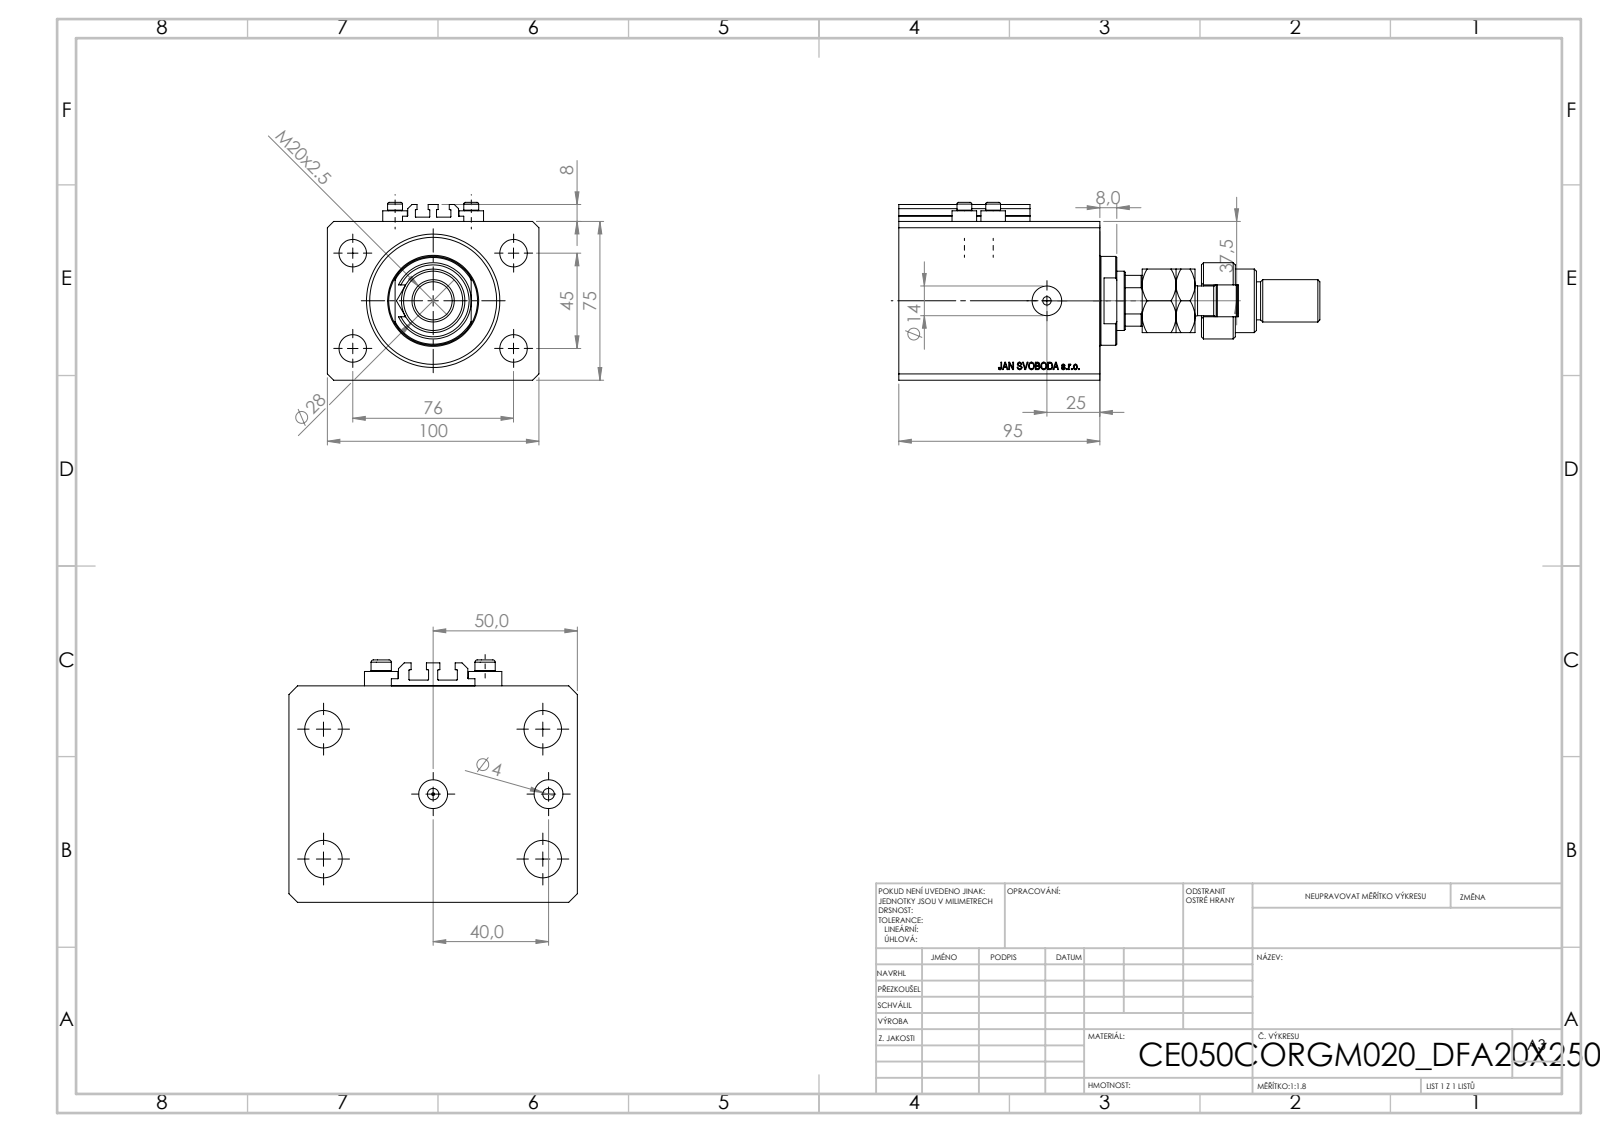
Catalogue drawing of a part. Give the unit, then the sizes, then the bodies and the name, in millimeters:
Units: millimetres
Overall size (bounding box): 199 × 100 × 84
Round holes (diameter × count): ⌀4 ×8, ⌀13 ×4, ⌀10 ×2, ⌀14 ×2, ⌀1.25 ×1, ⌀18.5 ×1, ⌀28 ×1, ⌀50 ×1, ⌀63 ×1
Round bosses / shafts (diameter × count): ⌀11.6 ×4, ⌀7 ×4, ⌀42 ×1, ⌀36 ×1, ⌀30 ×1, ⌀22 ×1, ⌀20 ×1, ⌀18 ×1
Partial cylindrical surfaces — rounded edges, fillets, slot ends (radius × count): R0.2 ×10, R7.5 ×1, R12 ×1, R13.5 ×1
Main face-to-face distances: 75, 100, 20, 95, 11.9, 83.1, 63.1, 40, 30, 55
Hole centre spacings: 44.16, 45, 13.6, 22.59, 36, 38.48, 76, 81.18
Volume: 696 556 mm³ · Surface area: 130 719 mm²
Bodies: 10 solids, 1123 faces (532 planar, 101 cylindrical, 490 other)
Part name (STEP PRODUCT): MFA; V250CE_C_VCP; FEMALE_PART_FOR_DFA; ALLEN BOLT V250CE (+2 more)
STEP written by: SolidWorks 2019 (CONFIG_CONTROL_DESIGN)
